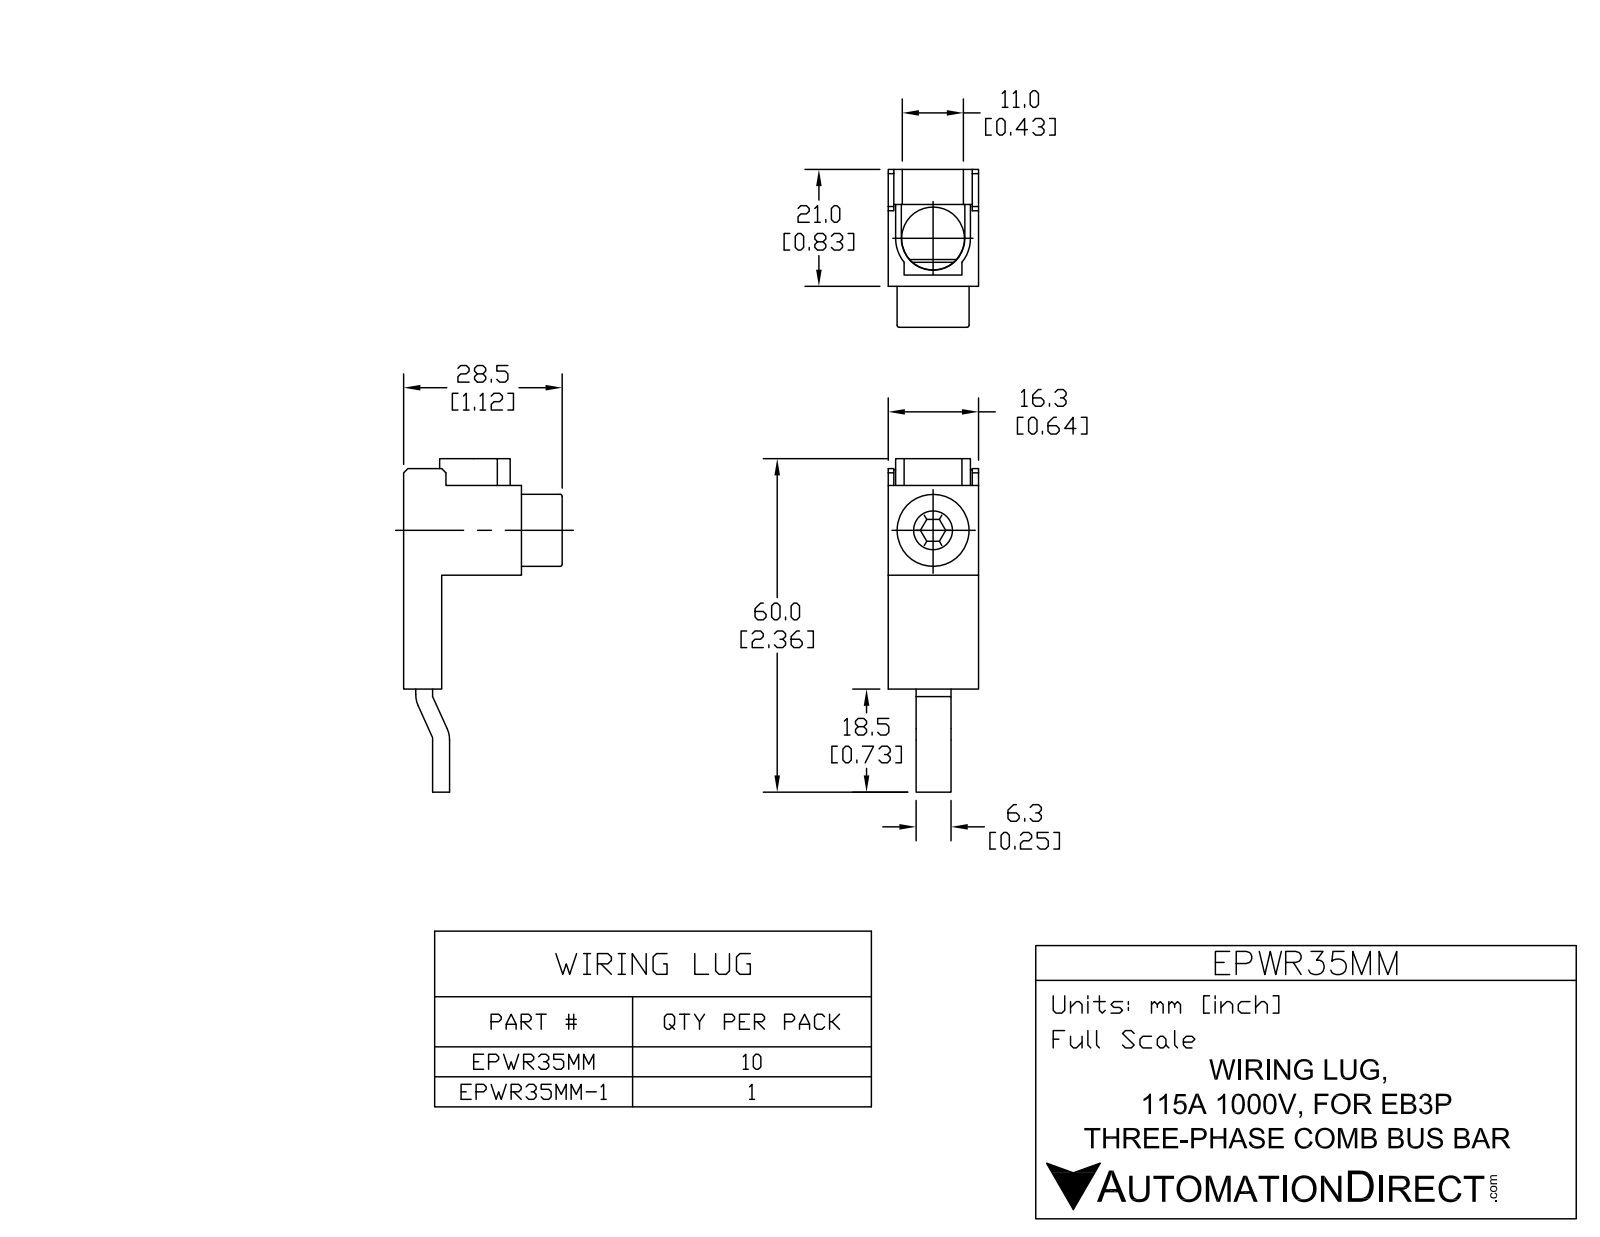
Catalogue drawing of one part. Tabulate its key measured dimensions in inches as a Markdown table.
| quantity | value |
| --- | --- |
| part name | EPWR35MM |
| STEP written by | SolidWorks 2011 (AUTOMOTIVE_DESIGN) |
| units | inches |
| bodies | 1 solid, 84 faces (62 planar, 19 cylindrical, 3 other) |
| overall size | 2.351 × 1.125 × 0.635 |
| volume | 0.466 in³ |
| surface area | 7.52 in² |
| round holes (diameter × count) | 0.275 × 1, 0.445 × 1 |
| round bosses / shafts (diameter × count) | 0.51 × 1 |
| partial cylindrical surfaces (radius × count) | 0.03 × 6, 0.2 × 2, 0.188 × 1, 0.225 × 1, 0.265 × 1 |
| main face-to-face distances | 0.635, 0.27, 0.197, 0.437, 0.12, 0.08, 0.835, 0.565, 0.24, 0.04 |
